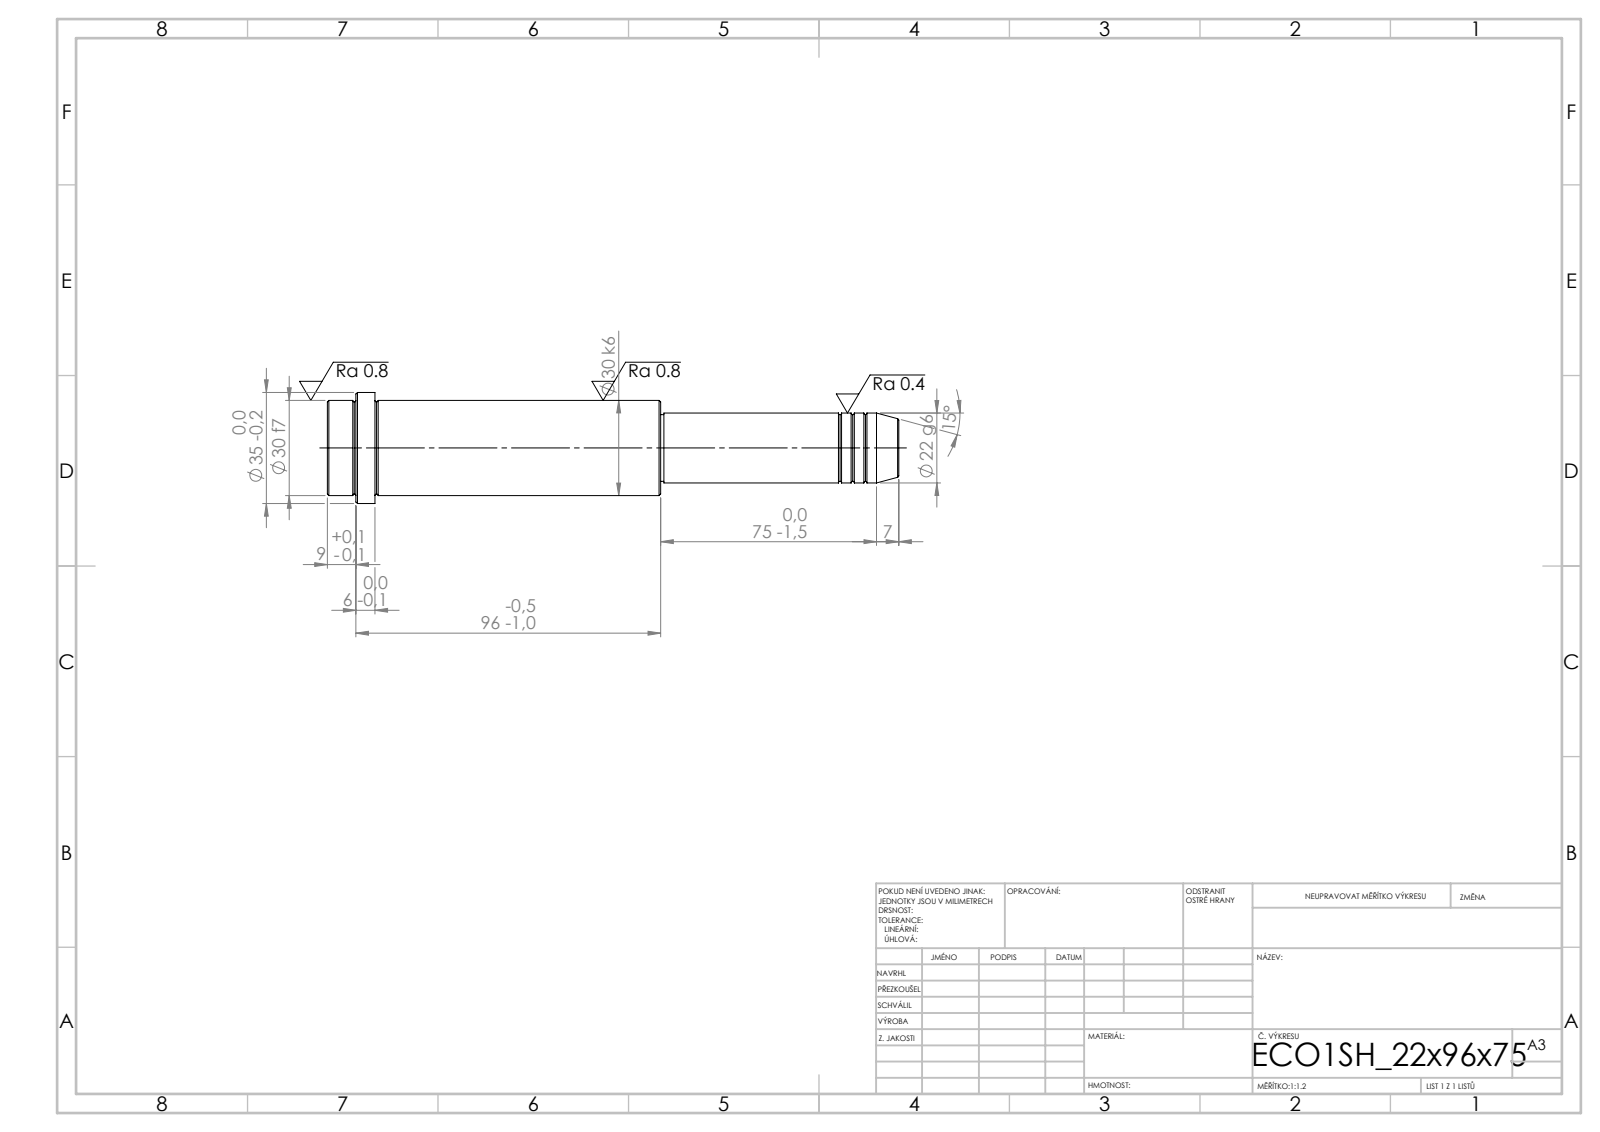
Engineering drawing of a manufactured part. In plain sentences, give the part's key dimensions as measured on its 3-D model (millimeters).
Its 3-D file was written by "SolidWorks 2019 (CONFIG_CONTROL_DESIGN)". It is 1 solid with 52 faces: 6 planar, 16 cylindrical and 30 other. Overall it measures 180 by 35 by 35 millimeters. Its volume is 103 609 cubic millimeters and its surface area 17 134 square millimeters. Round bosses or shafts: 1 of diameter 35, 1 of diameter 30, 1 of diameter 22, 1 of diameter 21. The main face-to-face distances are 105, 90, 15, 75, 165, 180, 171, 96, 6, 9.
